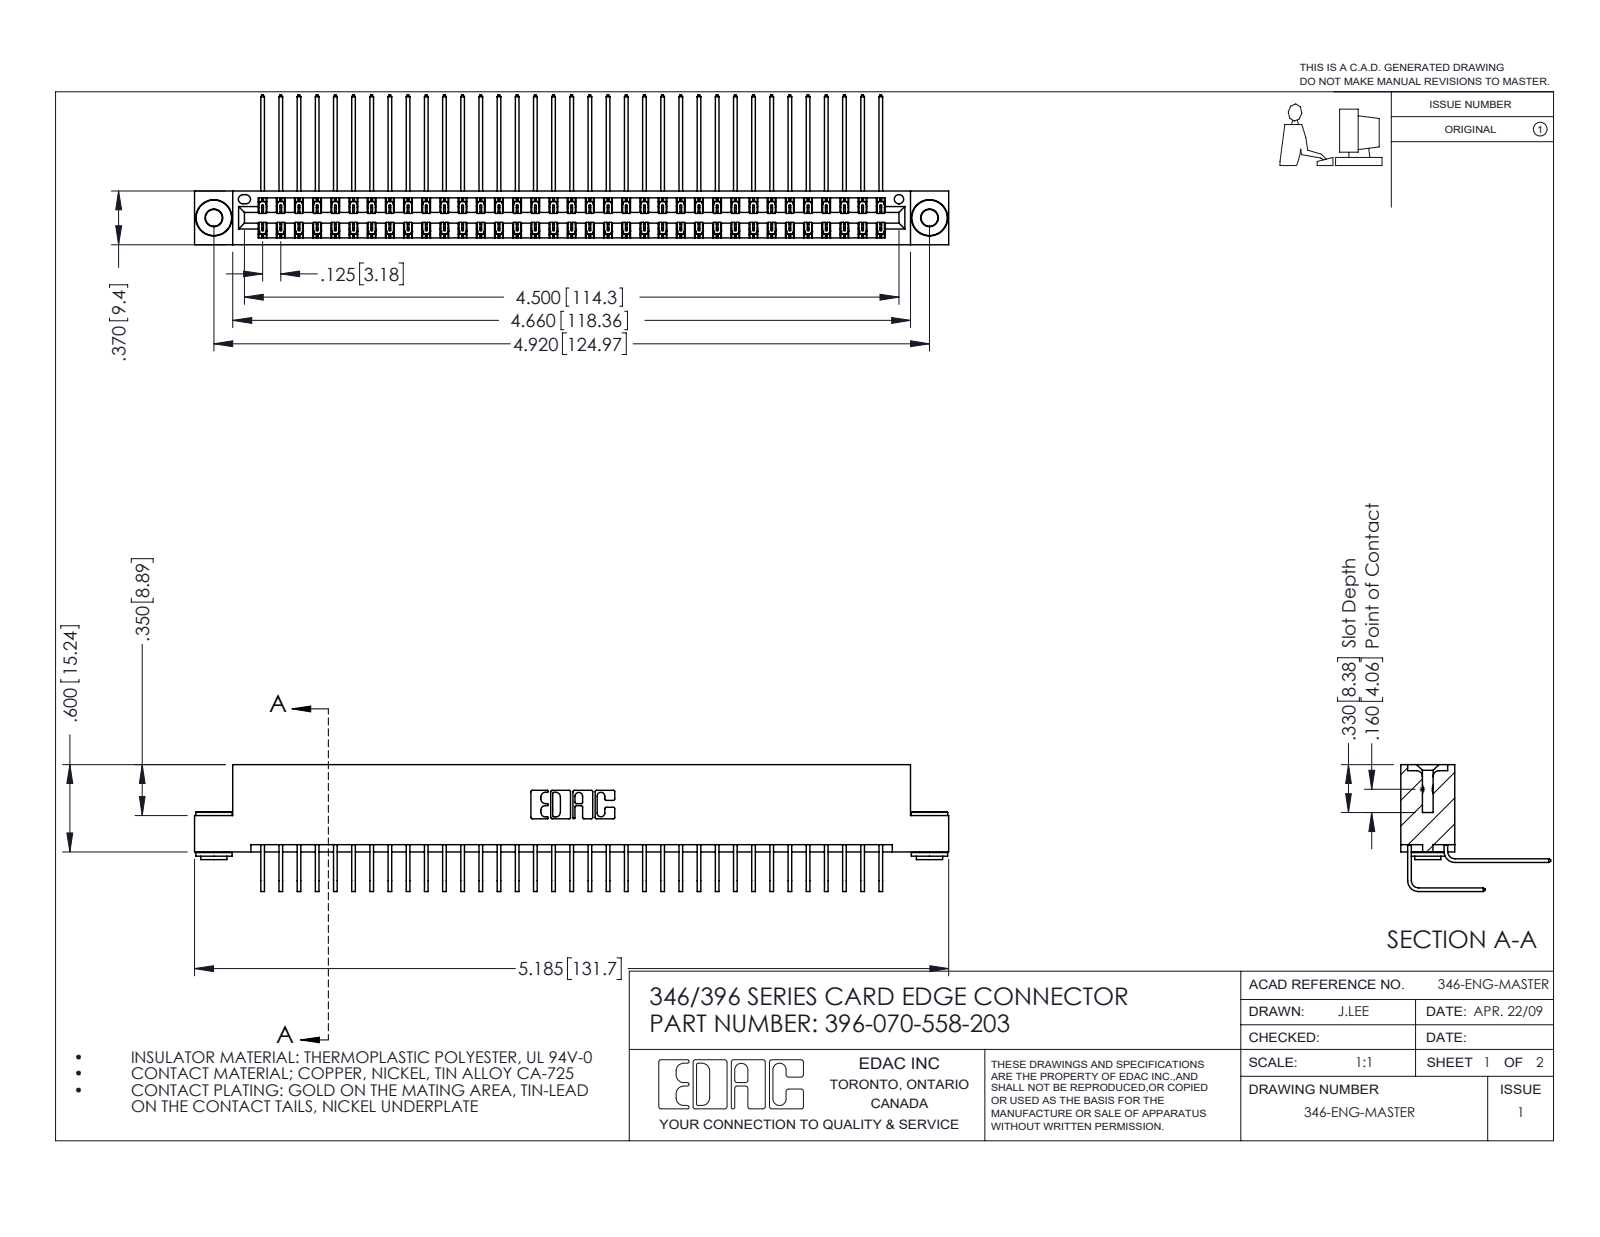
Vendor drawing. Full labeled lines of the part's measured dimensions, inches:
Part name (STEP PRODUCT): 345-292-001_558 Tail - 2; 345-250-002_345-250-002-102; 346 Part_Flush Mounting Lugs - 0.156 Dia-TH; 396-070-558-203 (+1 more)
STEP written by: SolidWorks 2016 (CONFIG_CONTROL_DESIGN)
Units: inches
Bodies: 73 solids, 3940 faces (2676 planar, 1256 cylindrical, 8 other)
Overall size (bounding box): 5.185 × 1.03 × 0.873
Volume: 0.806 in³ · Surface area: 31.31 in²
Round holes (diameter × count): ⌀0.116 ×2, ⌀0.156 ×2, ⌀0.064 ×1
Round bosses / shafts (diameter × count): ⌀0.25 ×2, ⌀0.18 ×2, ⌀0.136 ×2
Partial cylindrical surfaces — rounded edges, fillets, slot ends (radius × count): R0.006 ×105, R0.01 ×22, R0.007 ×6, R0.031 ×6, R0.026 ×3, R0.014 ×2, R0.022 ×2, R0.024 ×2
Main face-to-face distances: 0.322, 0.048, 0.025, 0.25, 0.37, 0.298, 0.072, 0.275, 0.148, 0.222
Hole centre spacings: 0.246, 4.711, 4.92
